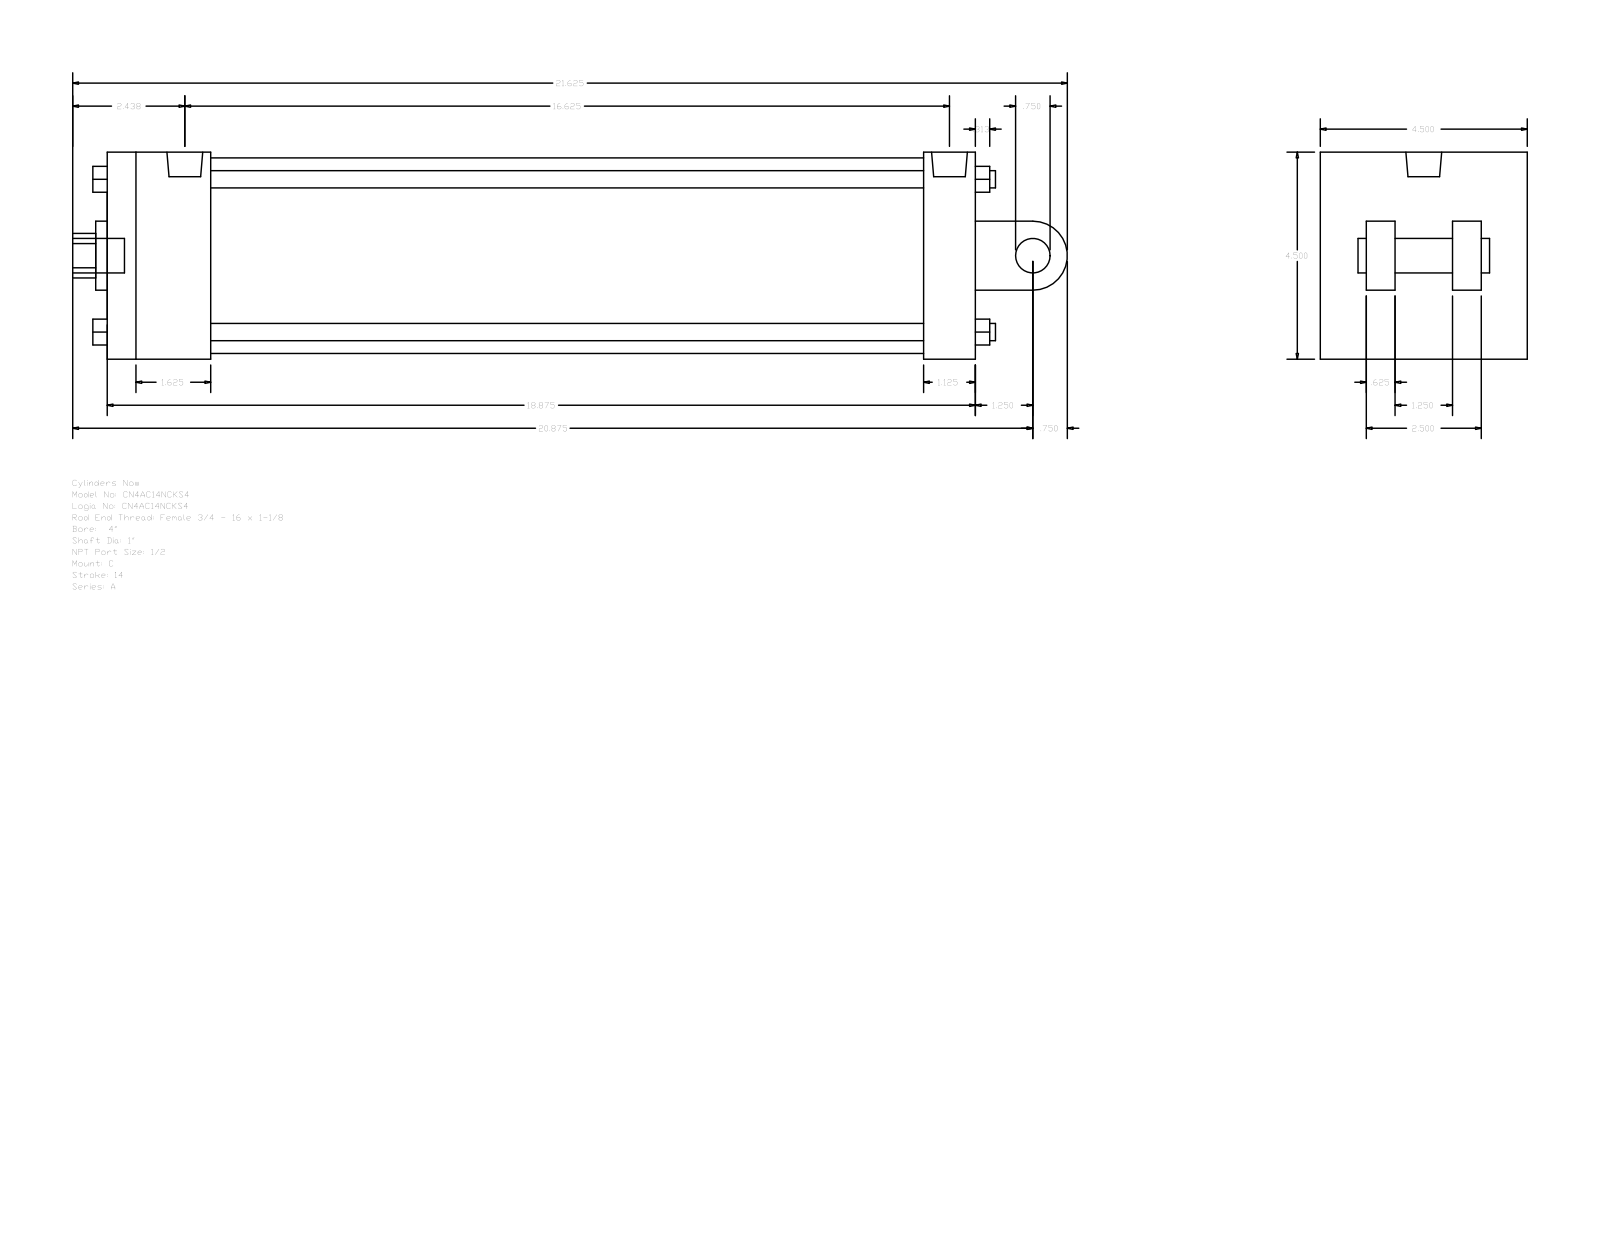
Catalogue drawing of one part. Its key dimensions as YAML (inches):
part_name: "A_C__0400_1"
step_written_by: "GSSL Pune (CONFIG_CONTROL_DESIGN)"
units: inches
bodies: {solids: 0, faces: 135, planar: 102, cylindrical: 33, other: 0}
overall_size: [21.625, 4.5, 4.5]
round_holes:
  - {diameter: 0.344, count: 2}
  - {diameter: 0.778, count: 1}
  - {diameter: 1, count: 1}
  - {diameter: 1.5, count: 1}
  - {diameter: 4.25, count: 1}
round_bosses_or_shafts:
  - {diameter: 0.375, count: 4}
  - {diameter: 0.75, count: 2}
  - {diameter: 0.344, count: 2}
  - {diameter: 0.778, count: 1}
partial_cylinders:
  - {radius: 0.484, count: 1}
  - {radius: 0.75, count: 1}
face_to_face_distances: [4.5, 18.875, 2.875, 17.75, 1.125, 2.25, 15.5, 16.625, 0.625, 1.875]
hole_center_spacings: [0.125]
